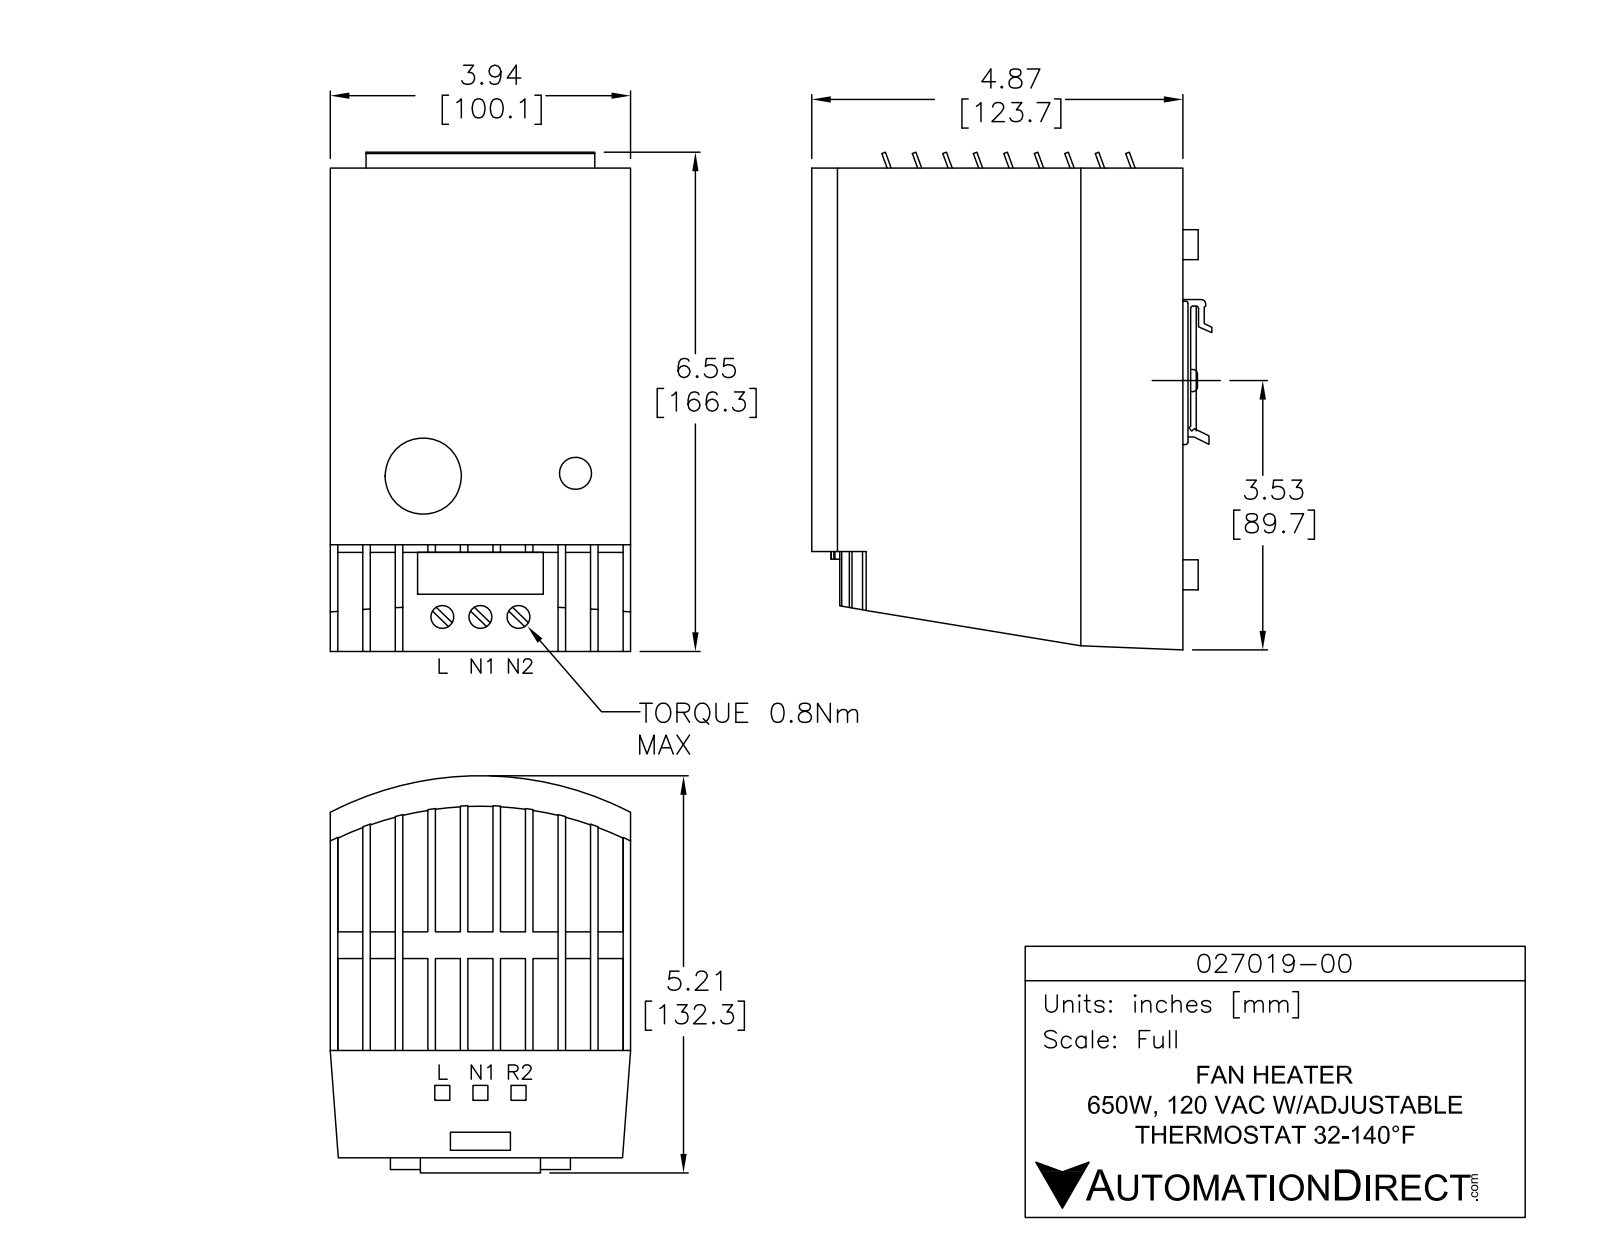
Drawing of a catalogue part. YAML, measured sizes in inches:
part_name: "027019-00"
step_written_by: "SolidWorks 2013 (AUTOMOTIVE_DESIGN)"
units: inches
bodies: {solids: 1, faces: 348, planar: 254, cylindrical: 41, other: 53}
overall_size: [6.579, 5.243, 3.92]
volume: 95.72
surface_area: 234
round_holes:
  - {diameter: 0.26, count: 3}
  - {diameter: 0.33, count: 1}
round_bosses_or_shafts:
  - {diameter: 0.29, count: 1}
partial_cylinders:
  - {radius: 0.03, count: 18}
  - {radius: 0.032, count: 4}
  - {radius: 0.033, count: 4}
  - {radius: 0.06, count: 1}
  - {radius: 6.254, count: 1}
face_to_face_distances: [0.377, 0.754, 0.489, 3.916, 0.111, 1.131, 0.275, 0.754, 1.131, 1.508]
hole_center_spacings: [0.4, 0.8, 1.876, 2.059, 2.298]
